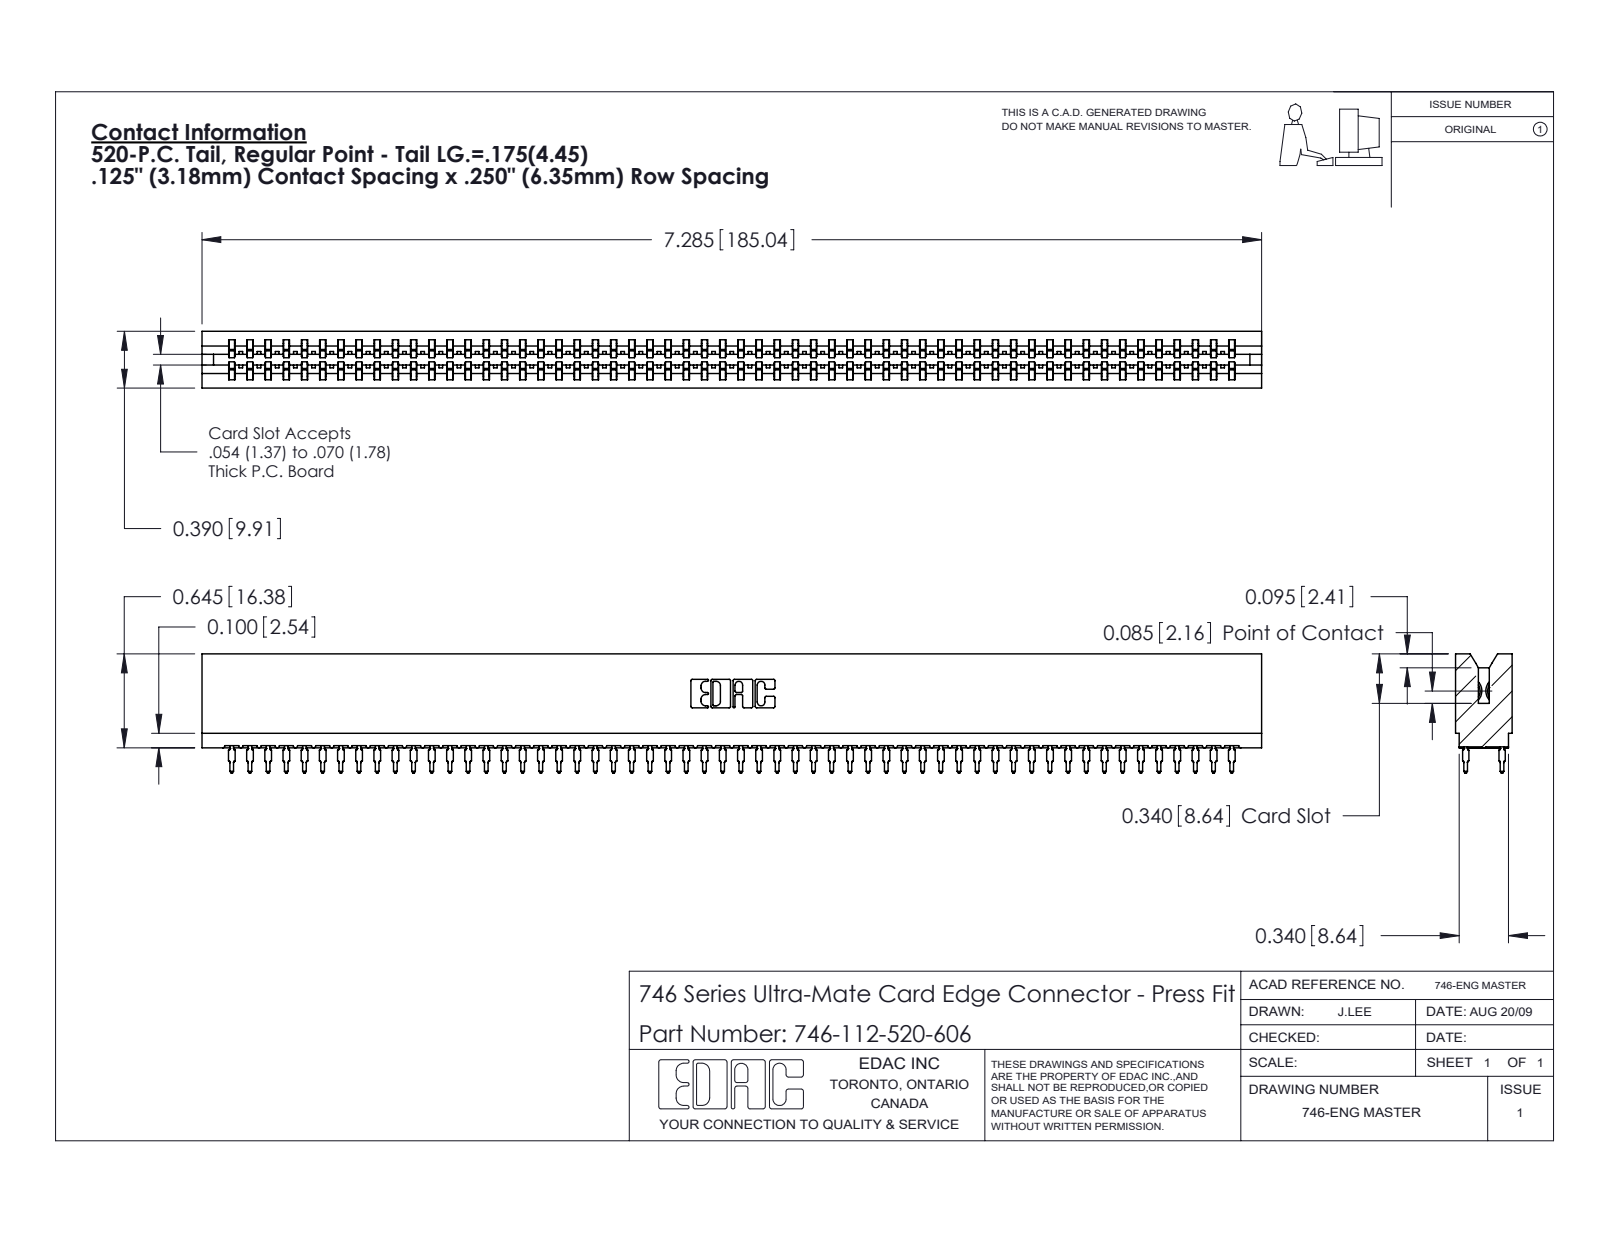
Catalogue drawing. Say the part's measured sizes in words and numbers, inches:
The part is named "746 Part_.340 Slot Depth - 06; 746-112-520-606; 746-292-001_520". Its 3-D file was written by "SolidWorks 2020 (CONFIG_CONTROL_DESIGN)". It is 113 solids with 10122 faces: 5208 planar, 2002 cylindrical and 2912 other. Overall it measures 7.285 by 0.819 by 0.39 inches. Its volume is 1.287 cubic inches and its surface area 47.5 square inches. Partial cylindrical surfaces (rounded edges, fillets, slot ends): 224 of radius 0.021, 57 of radius 0.015, 22 of radius 0.01, 8 of radius 0.005, 8 of radius 0.011, 6 of radius 0.007, 6 of radius 0.031, 3 of radius 0.026. The main face-to-face distances are 0.057, 0.333, 0.39, 0.025, 0.25, 0.307, 0.275, 0.083, 0.015, 0.5.
